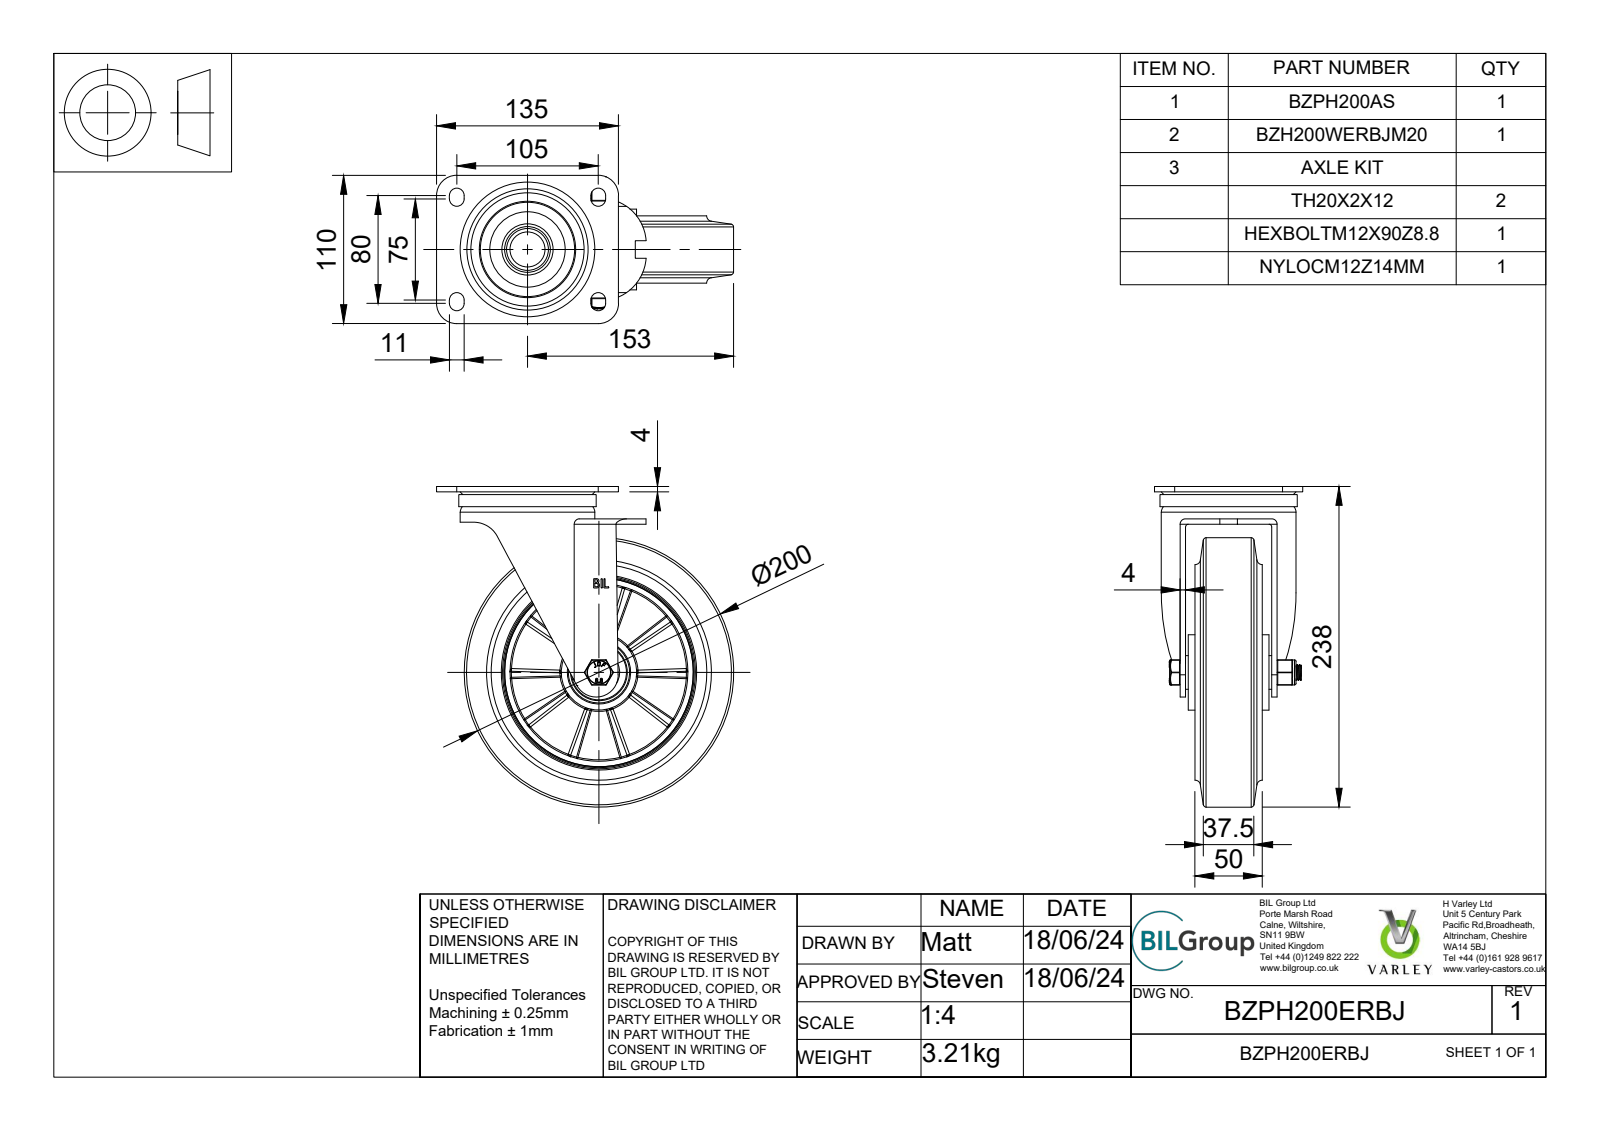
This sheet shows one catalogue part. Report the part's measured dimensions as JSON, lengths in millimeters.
{"part_name": "BZPH200ERBJ v3; BZH200WERBJM20 v1; 65 SHORE A ELASTIC RUBBER TYRE; ALUMINIUM RIM (+7 more)", "step_written_by": "Autodesk Translation Framework v13.14.0.145 (AUTOMOTIVE_DESIGN)", "units": "millimeters", "bodies": {"solids": 38, "faces": 1335, "planar": 461, "cylindrical": 215, "other": 659}, "overall_size": [238, 220.5, 110], "volume_mm3": 1163000, "surface_area_mm2": 344535, "round_holes": [[42, 2], [12, 1], [12.2, 1], [12.5, 1], [14, 1], [20, 1], [26, 1], [28.5, 1], [30.8, 1], [40.3, 1], [40.5, 1], [44, 1]], "round_bosses_or_shafts": [[200, 1], [141.5, 1], [101.95, 1], [100, 1], [73, 1], [56, 1], [50, 1], [40.8, 1]], "partial_cylinders_radius": [[0.5, 18], [5.5, 8], [0.47, 4], [0.9, 4], [15, 4], [0.89, 2], [0.89, 2], [2, 2]], "face_to_face_distances": [7, 4, 50, 11, 3, 17, 9, 13, 18, 14]}
